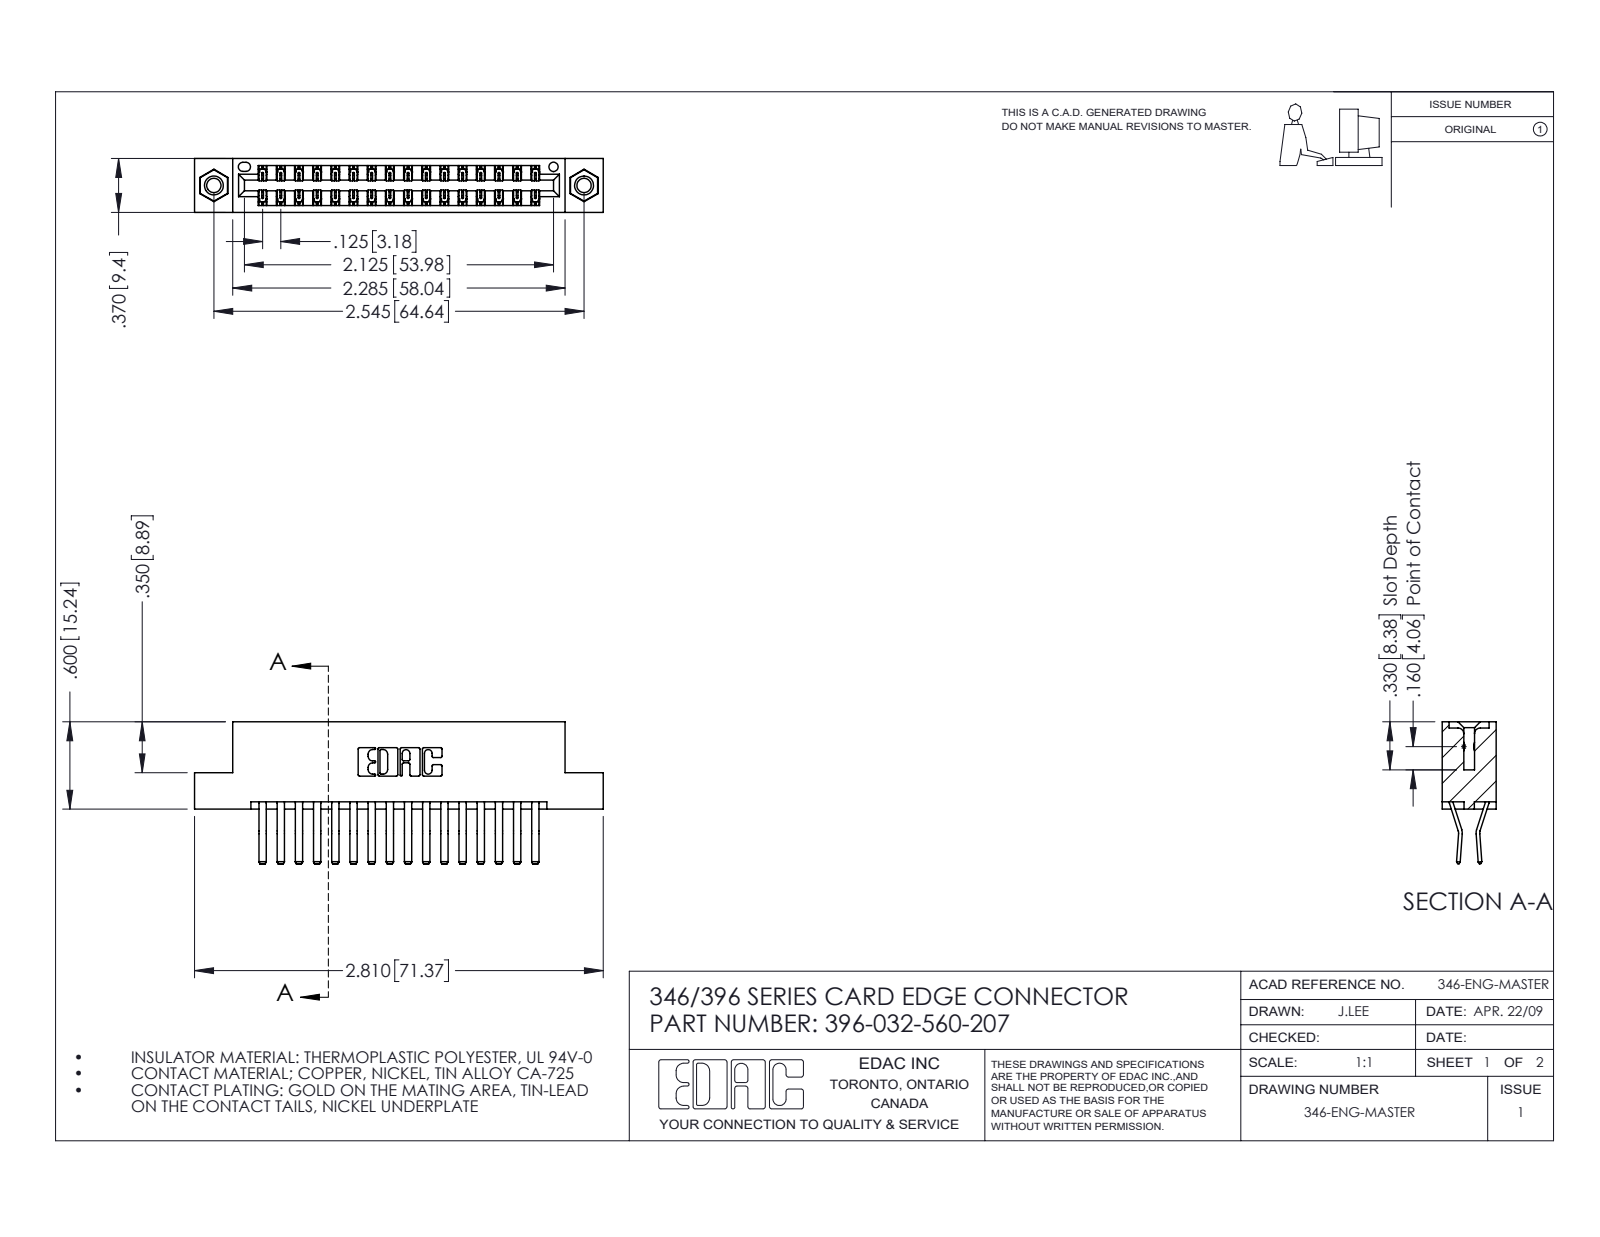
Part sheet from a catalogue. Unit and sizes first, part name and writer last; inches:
Units: inches
Overall size (bounding box): 2.81 × 0.975 × 0.37
Round holes (diameter × count): ⌀0.098 ×2, ⌀0.125 ×2, ⌀0.156 ×2, ⌀0.064 ×1
Round bosses / shafts (diameter × count): ⌀0.155 ×2
Partial cylindrical surfaces — rounded edges, fillets, slot ends (radius × count): R0.006 ×48, R0.01 ×22, R0.007 ×6, R0.031 ×6, R0.026 ×3, R0.01 ×2, R0.014 ×2, R0.022 ×2
Main face-to-face distances: 0.048, 0.322, 0.25, 0.37, 0.025, 0.072, 0.298, 0.275, 0.148, 0.222
Hole centre spacings: 0.246, 2.338, 2.545
Volume: 0.424 in³ · Surface area: 15.1 in²
Bodies: 35 solids, 1910 faces (1228 planar, 666 cylindrical, 16 other)
Part name (STEP PRODUCT): 396-032-560-207; 346 Part_Flush Mounting Lugs - 0.156 Dia-TI; 345-292-001_560 Tail; 345-250-001_345-250-005-103
STEP written by: SolidWorks 2016 (CONFIG_CONTROL_DESIGN)
